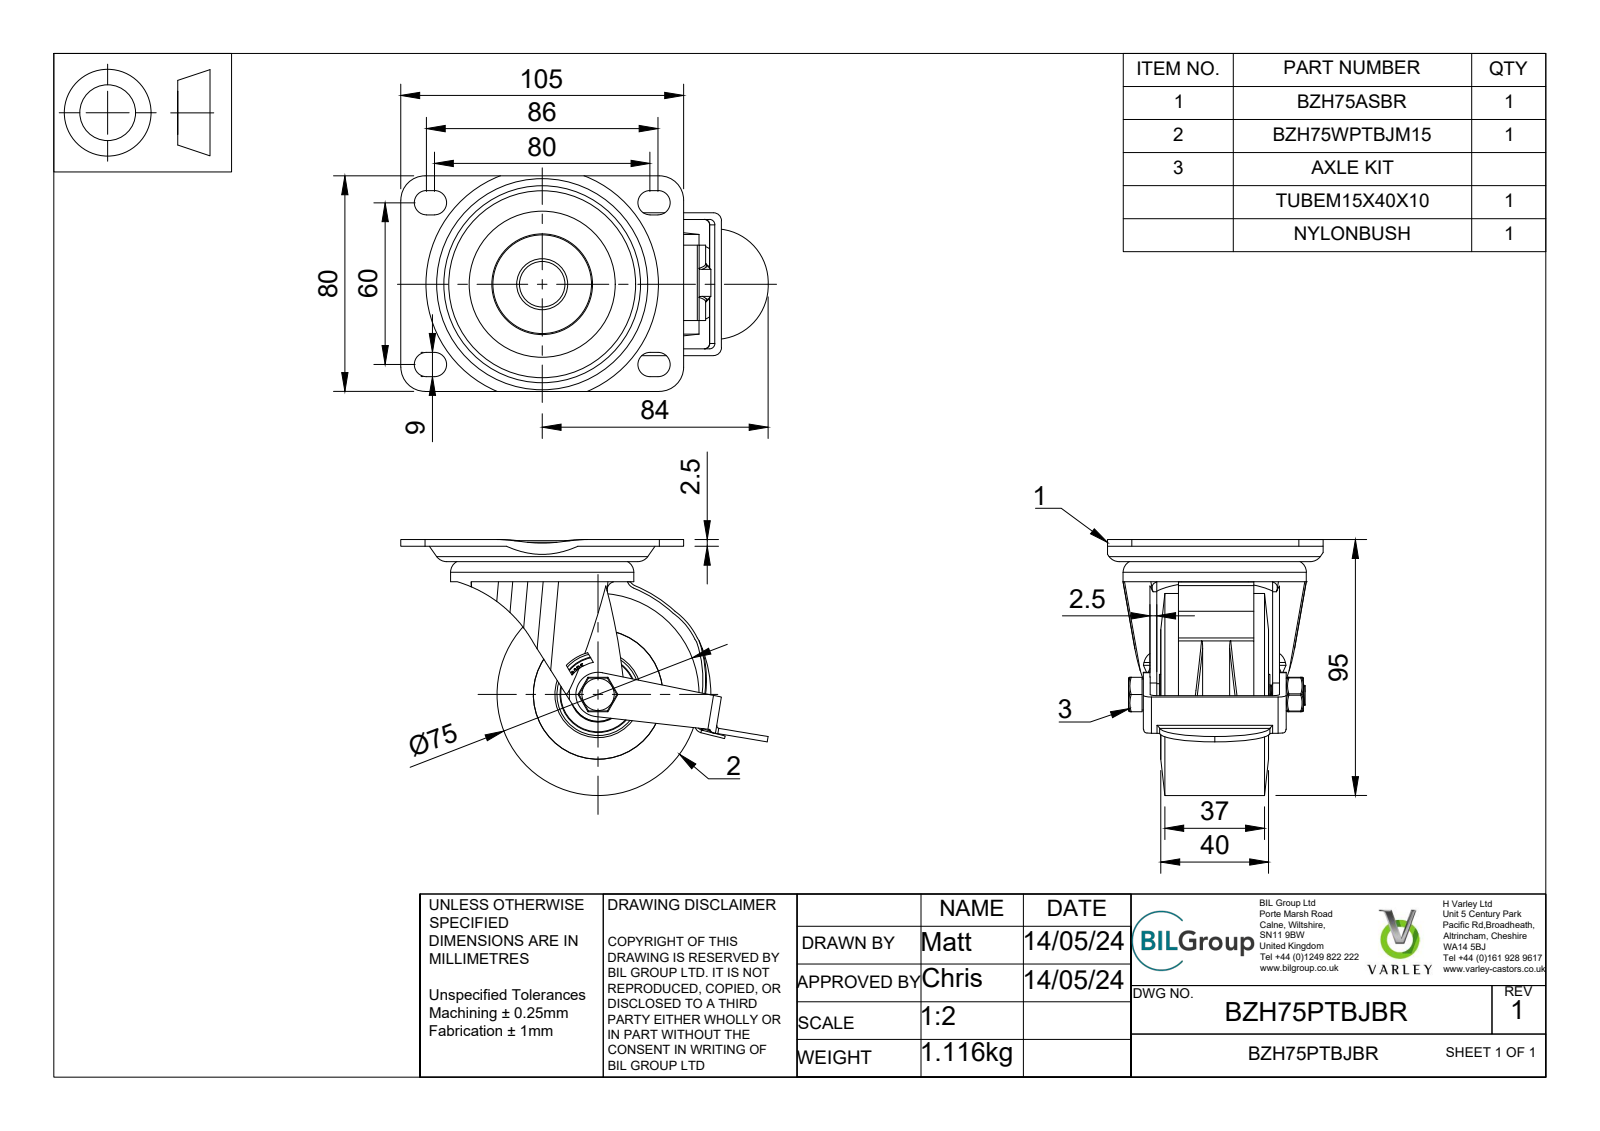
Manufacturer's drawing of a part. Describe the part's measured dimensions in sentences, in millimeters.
The part is named "BZH75PTBJBR v2; BZH75ASBR v1; ZINC PLATED, PRESSED STEEL TOP PLATE; ZINC PLATED, PRESSED STEEL FORKS (+8 more)". Its 3-D file was written by "Autodesk Translation Framework v13.14.0.145 (AUTOMOTIVE_DESIGN)". It is 39 solids with 1092 faces: 350 planar, 203 cylindrical and 539 other. Overall it measures 136.37 by 95 by 80 millimeters. Its volume is 216 511 cubic millimeters and its surface area 104 589 square millimeters. Round holes: 1 of diameter 8, 1 of diameter 8.2, 1 of diameter 10.2, 1 of diameter 14, 1 of diameter 15, 1 of diameter 20.5, 1 of diameter 26.8, 1 of diameter 28, 1 of diameter 28.2, 1 of diameter 32, 1 of diameter 37.4, 1 of diameter 48. Round bosses or shafts: 1 of diameter 75, 1 of diameter 68, 1 of diameter 24, 1 of diameter 21.5, 1 of diameter 20, 1 of diameter 19, 1 of diameter 18.91, 1 of diameter 18. Partial cylindrical surfaces (rounded edges, fillets, slot ends): 8 of radius 4.5, 7 of radius 3, 6 of radius 0.5, 5 of radius 1, 4 of radius 2, 4 of radius 9, 2 of radius 4, 2 of radius 4.3. The main face-to-face distances are 2.5, 1.5, 0.4, 7.26, 4.04, 44.04, 31, 50.5, 2.4, 40.
